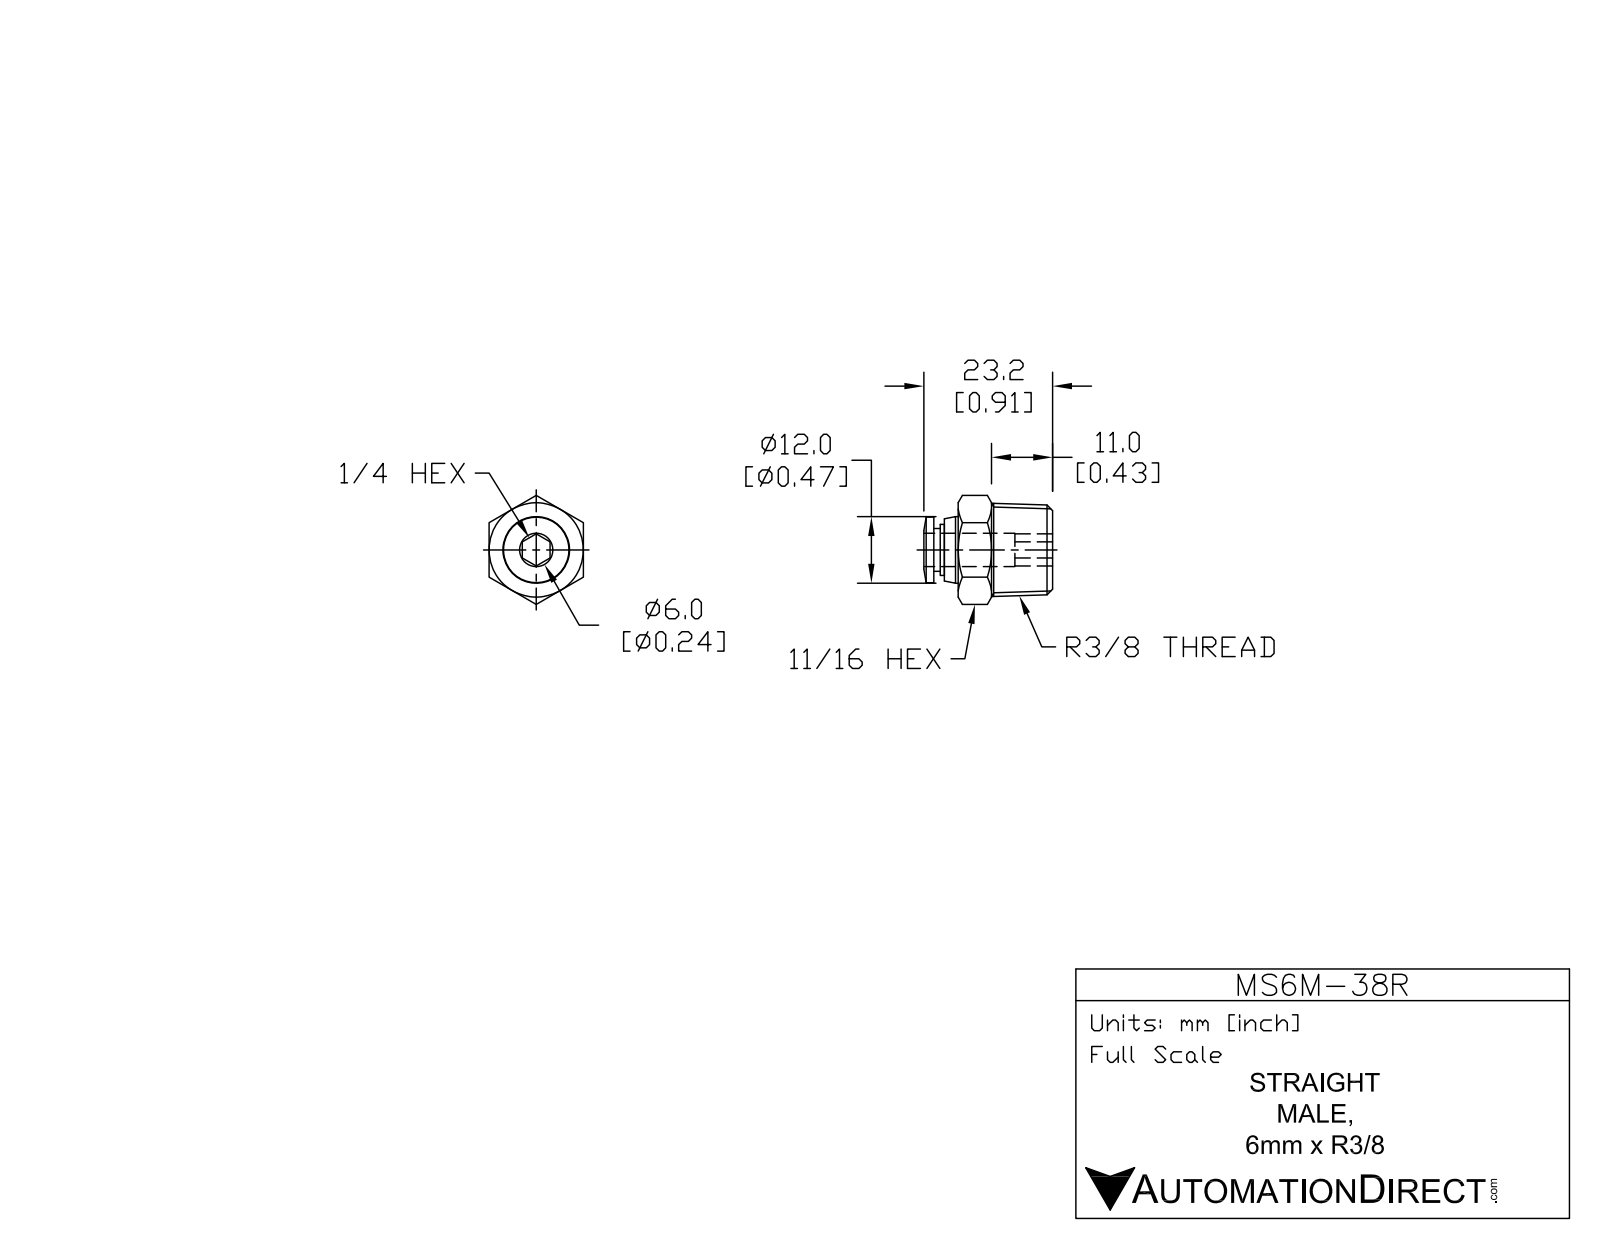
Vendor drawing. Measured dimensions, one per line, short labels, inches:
name: MS6M-38R
written by: SolidWorks 2015 (AUTOMOTIVE_DESIGN)
unit: in
bodies: 1 solid, 49 faces (14 planar, 12 cylindrical, 23 other)
size: 0.902 × 0.773 × 0.669
volume: 0.222 in³; area: 3.139 in²
holes: 1× ⌀0.197, 1× ⌀0.248
bosses: 1× ⌀0.472, 1× ⌀0.465, 1× ⌀0.362, 1× ⌀0.303
face distances: 0.669, 0.657, 0.831, 0.173, 0.756, 0.098, 0.075, 0.785, 0.128, 0.03
